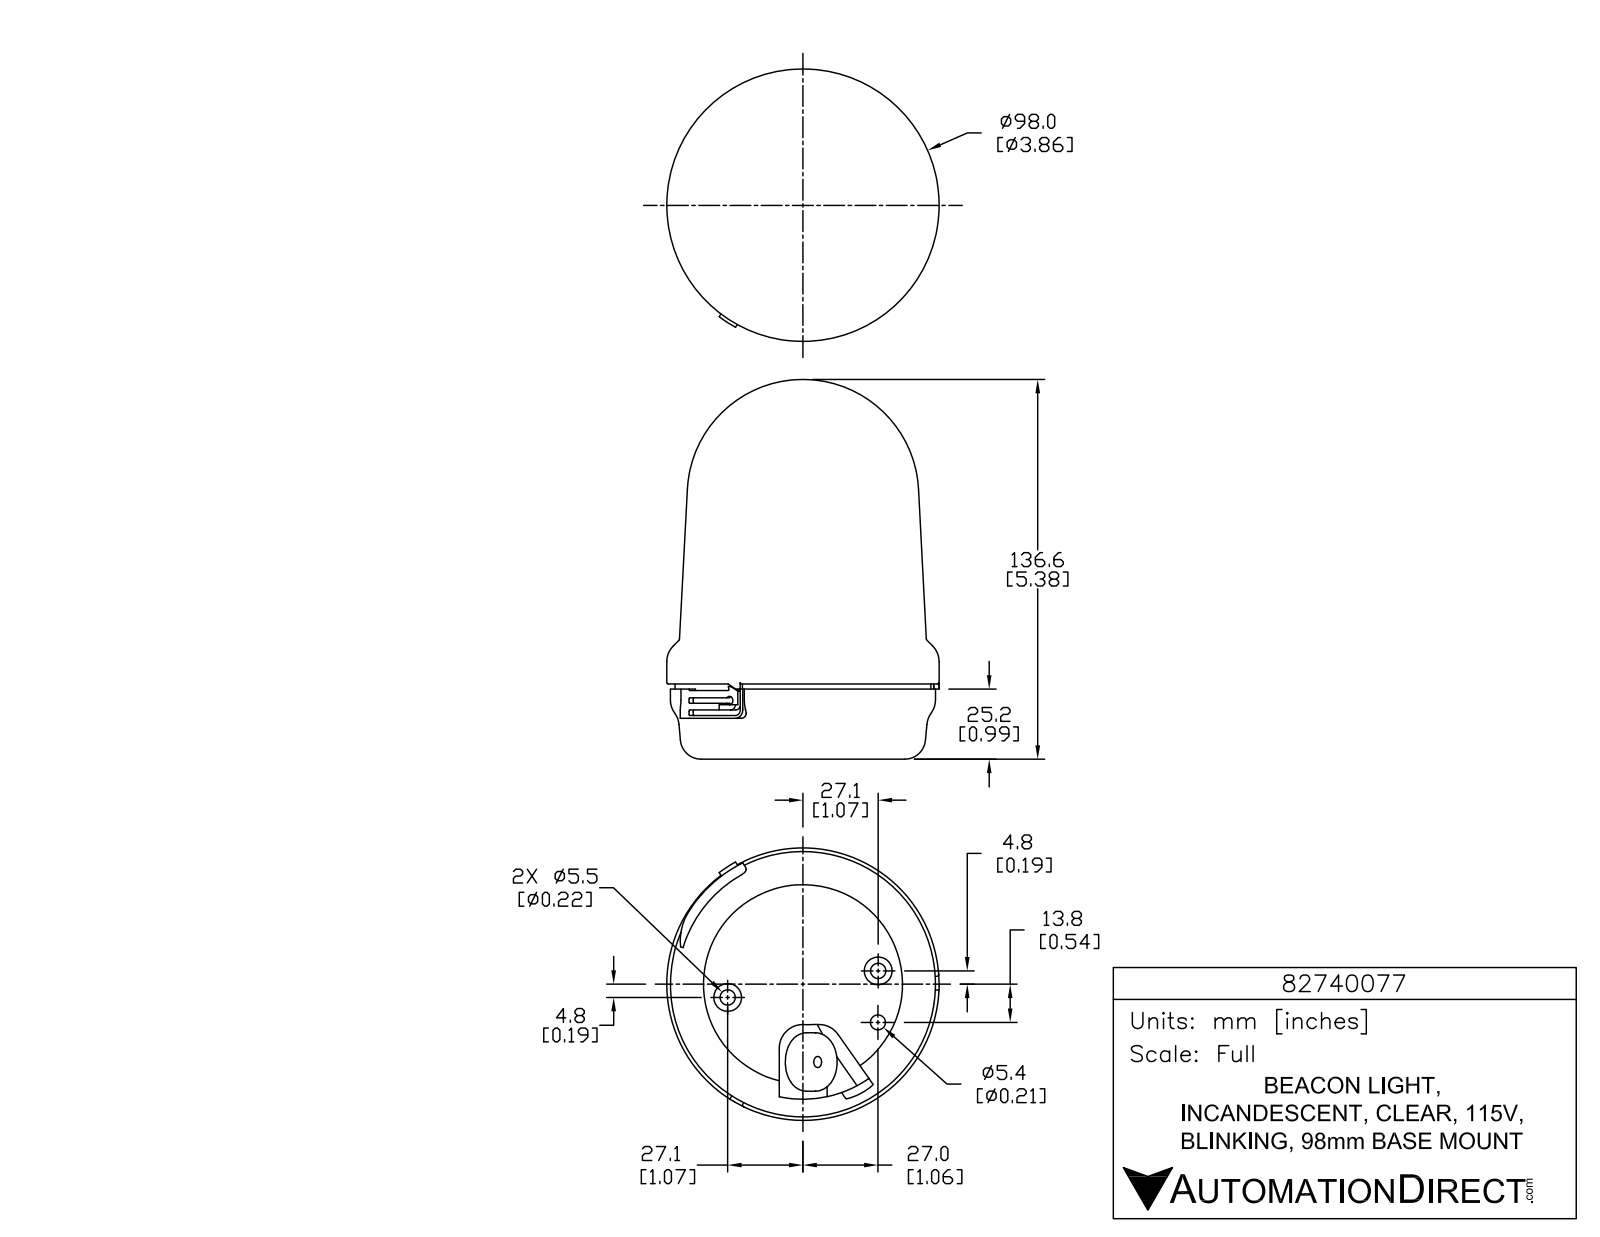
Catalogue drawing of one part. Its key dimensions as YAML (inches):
part_name: "82740077"
step_written_by: "SolidWorks 2015 (AUTOMOTIVE_DESIGN)"
units: inches
bodies: {solids: 1, faces: 872, planar: 566, cylindrical: 204, other: 102}
overall_size: [5.378, 3.858, 3.858]
volume: 44.69
surface_area: 73.66
round_holes:
  - {diameter: 0.059, count: 3}
  - {diameter: 0.217, count: 2}
  - {diameter: 0.157, count: 1}
  - {diameter: 0.213, count: 1}
  - {diameter: 2.819, count: 1}
round_bosses_or_shafts:
  - {diameter: 0.339, count: 3}
  - {diameter: 0.084, count: 3}
  - {diameter: 0.394, count: 2}
  - {diameter: 3.858, count: 1}
  - {diameter: 3.756, count: 1}
  - {diameter: 3.626, count: 1}
  - {diameter: 0.827, count: 1}
partial_cylinders:
  - {radius: 0.005, count: 9}
  - {radius: 0.005, count: 6}
  - {radius: 0.012, count: 6}
  - {radius: 0.012, count: 6}
  - {radius: 0.012, count: 6}
  - {radius: 0.196, count: 6}
  - {radius: 0.02, count: 5}
  - {radius: 0.039, count: 4}
face_to_face_distances: [1.045, 0.972, 0.073, 0.02, 0.992, 1.065, 0.236, 0.579, 0.559, 0.413]
hole_center_spacings: [1.083, 0.73, 1.193, 2.158, 2.165]
